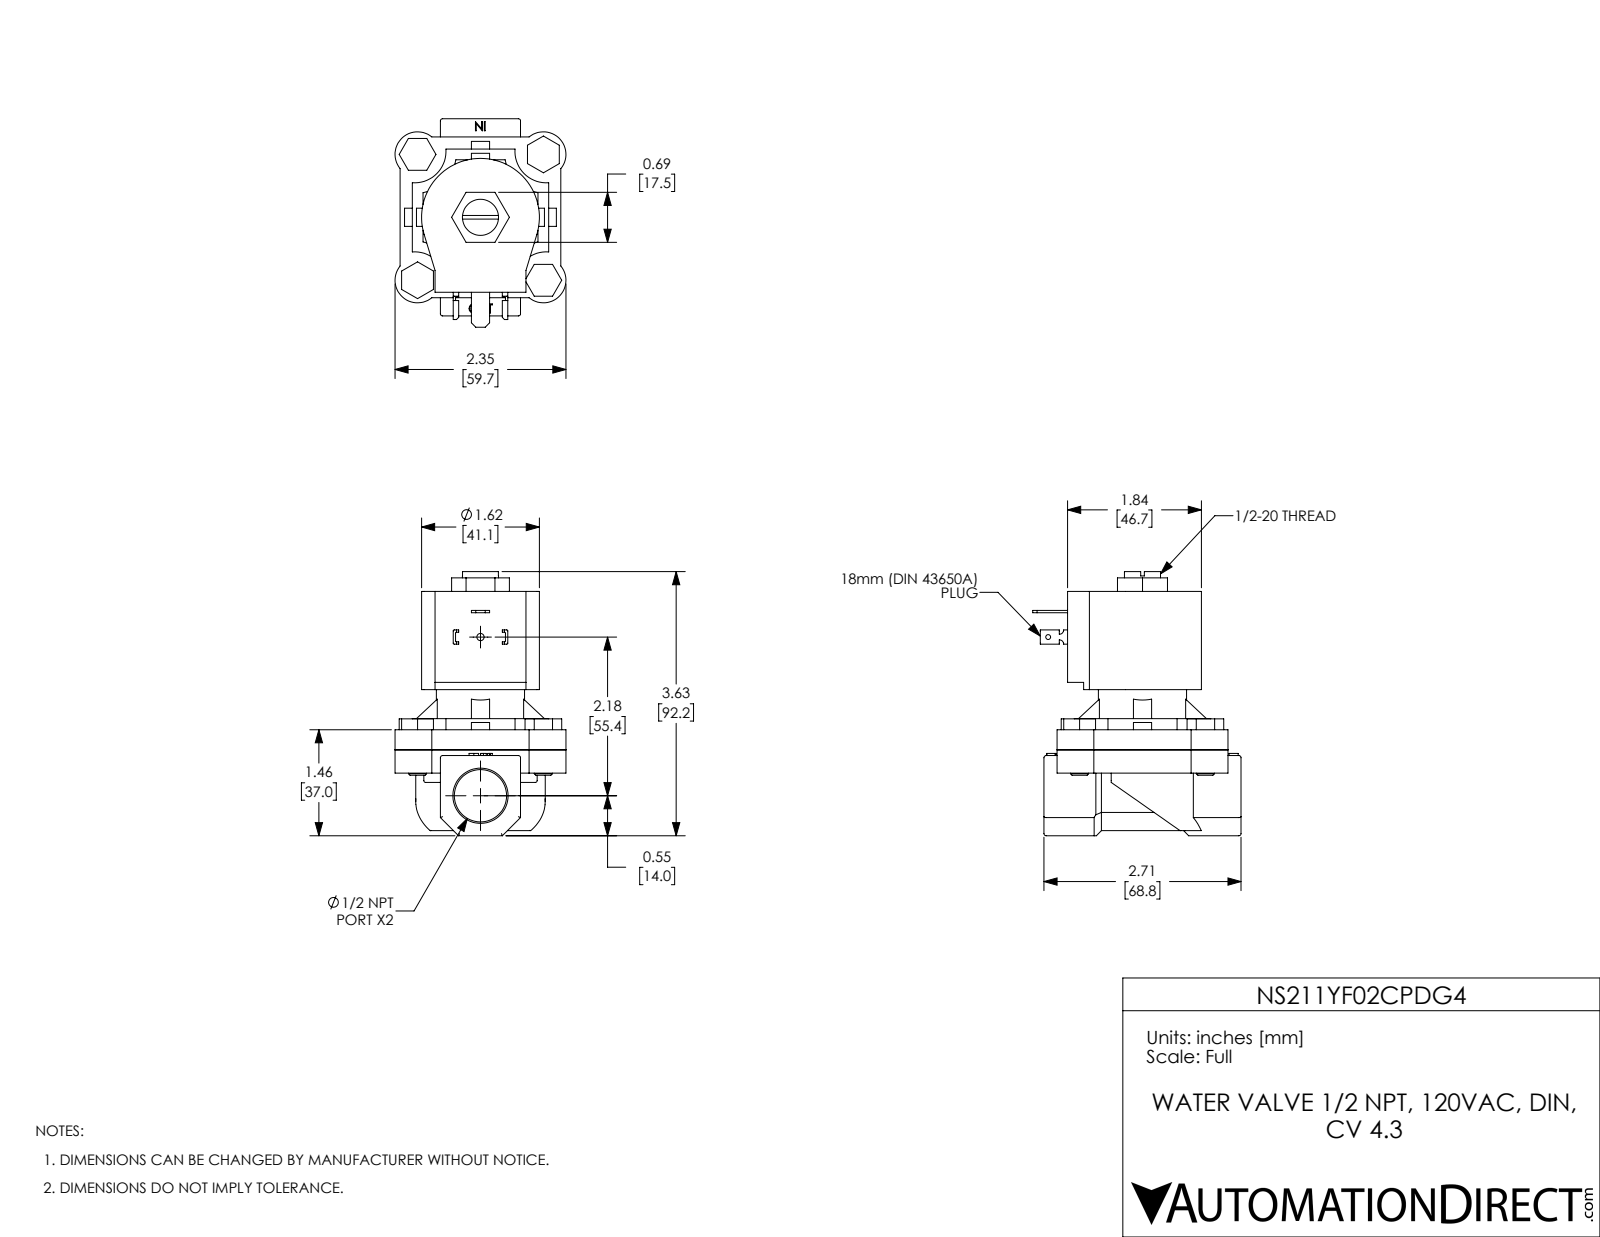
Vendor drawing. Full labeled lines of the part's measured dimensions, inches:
Part name (STEP PRODUCT): NS211YF02CPDG4
STEP written by: SolidWorks 2021 (CONFIG_CONTROL_DESIGN)
Units: inches
Bodies: 11 solids, 385 faces (239 planar, 113 cylindrical, 33 other)
Overall size (bounding box): 3.63 × 2.865 × 2.35
Volume: 9.473 in³ · Surface area: 65.14 in²
Round holes (diameter × count): ⌀0.25 ×4, ⌀0.067 ×1, ⌀0.1 ×1, ⌀0.496 ×1, ⌀0.512 ×1, ⌀0.719 ×1, ⌀1.155 ×1
Round bosses / shafts (diameter × count): ⌀0.248 ×4, ⌀1.213 ×1
Partial cylindrical surfaces — rounded edges, fillets, slot ends (radius × count): R0.03 ×15, R0.015 ×8, R0.31 ×4, R0.432 ×4, R0.579 ×4, R0.06 ×2, R0.81 ×1, R0.89 ×1
Main face-to-face distances: 0.276, 2.177, 1.901, 0.32, 0.596, 2.497, 0.554, 1.656, 0.25, 1.147
Hole centre spacings: 1.223, 1.73, 2.446, 2.181
